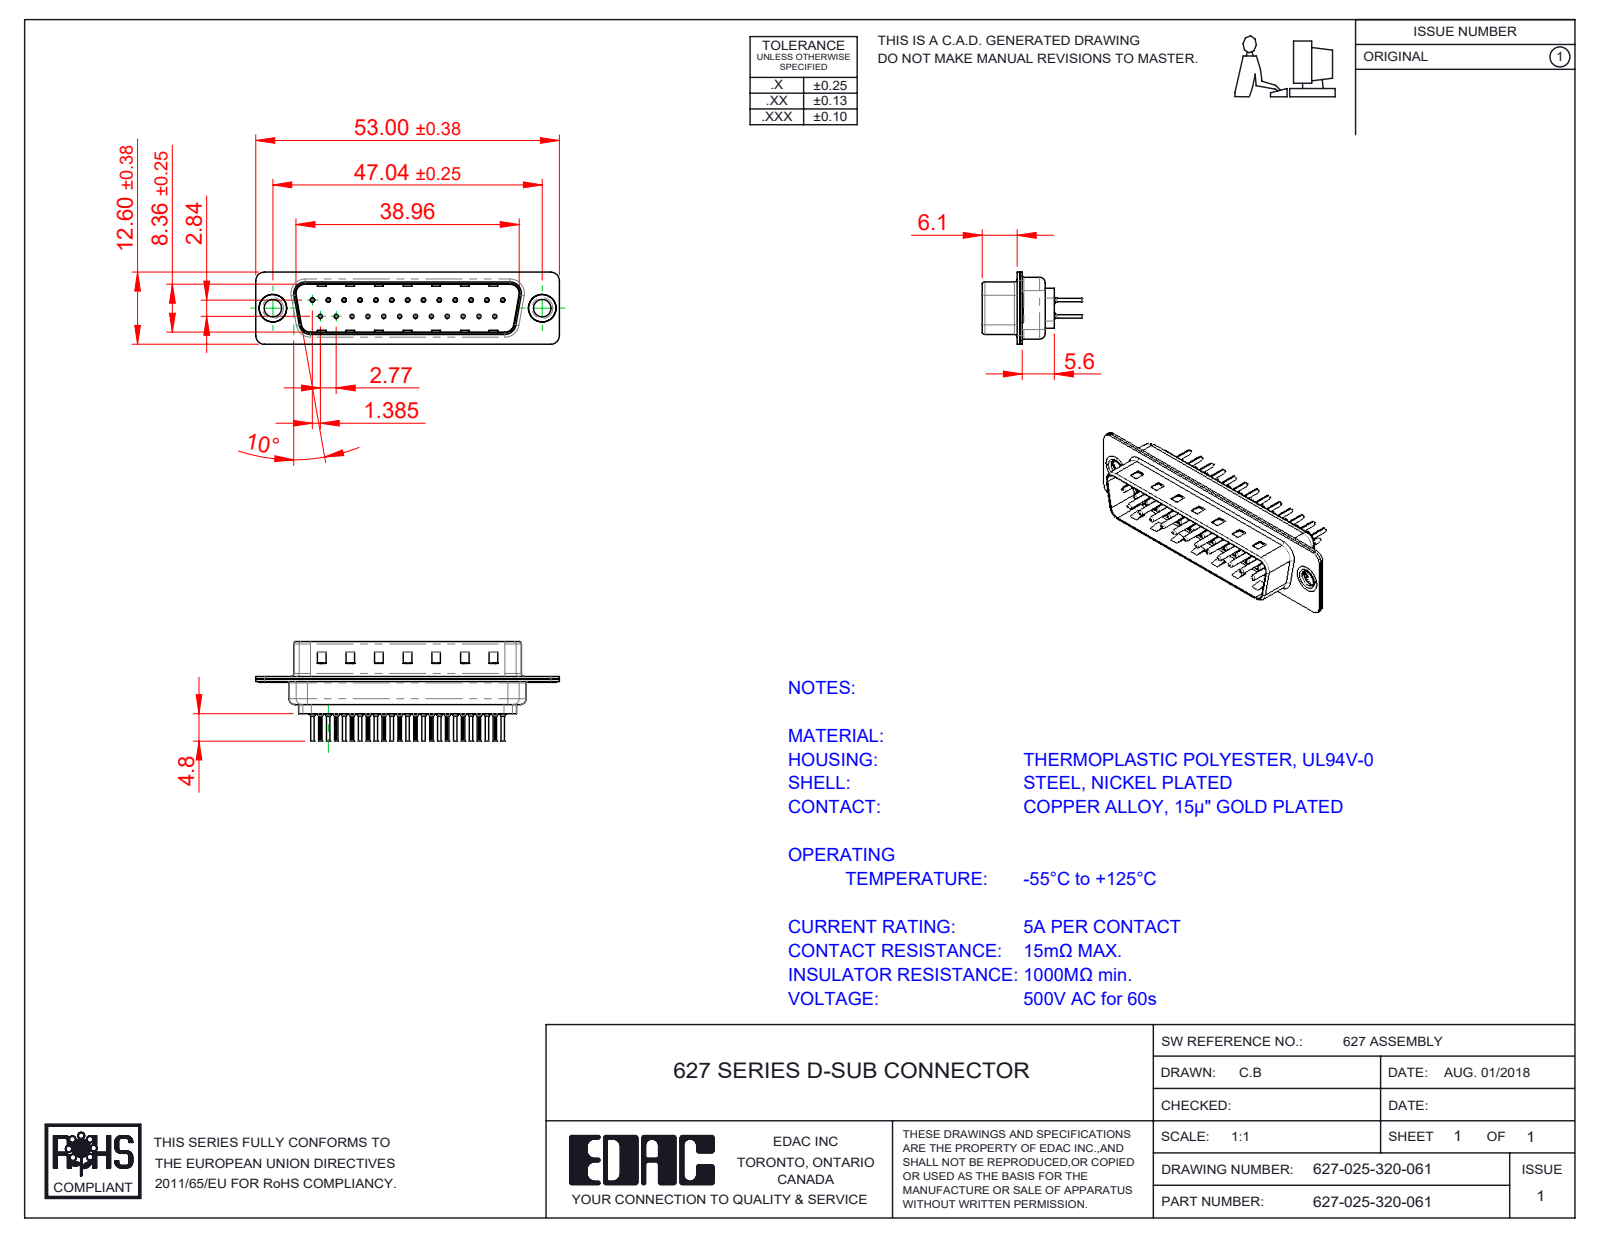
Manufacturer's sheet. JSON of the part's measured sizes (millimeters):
{"part_name": "627 Thru Hole Rivet; 627-025-320-061; 627 Contact Row 1_20L; 627 Contact Row 2_20L (+3 more)", "step_written_by": "SolidWorks 2020 (CONFIG_CONTROL_DESIGN)", "units": "millimeters", "bodies": {"solids": 30, "faces": 2800, "planar": 771, "cylindrical": 1046, "other": 983}, "overall_size": [53, 17.3, 12.6], "volume_mm3": 2604, "surface_area_mm2": 7660, "round_holes": [[0.2, 25], [0.35, 25], [1.1, 25], [1.6, 25], [3.05, 2], [4, 2], [4.8, 2]], "round_bosses_or_shafts": [[2, 25], [1.5, 25], [0.75, 25], [0.6, 25], [5, 2], [4.9, 2], [3.55, 2]], "partial_cylinders_radius": [[0.1, 50], [1.5, 16], [2, 12], [0.5, 8], [1.6, 8], [0.25, 4], [0.6, 4], [0.65, 4]], "face_to_face_distances": [0.4, 0.45, 0.82, 9.58, 0.9, 8.76, 1.5, 1.4, 6.5, 6.05], "hole_center_spacings": [3.16, 8.31, 2.77, 5.54, 11.08, 16.62, 5.03, 5.04]}
